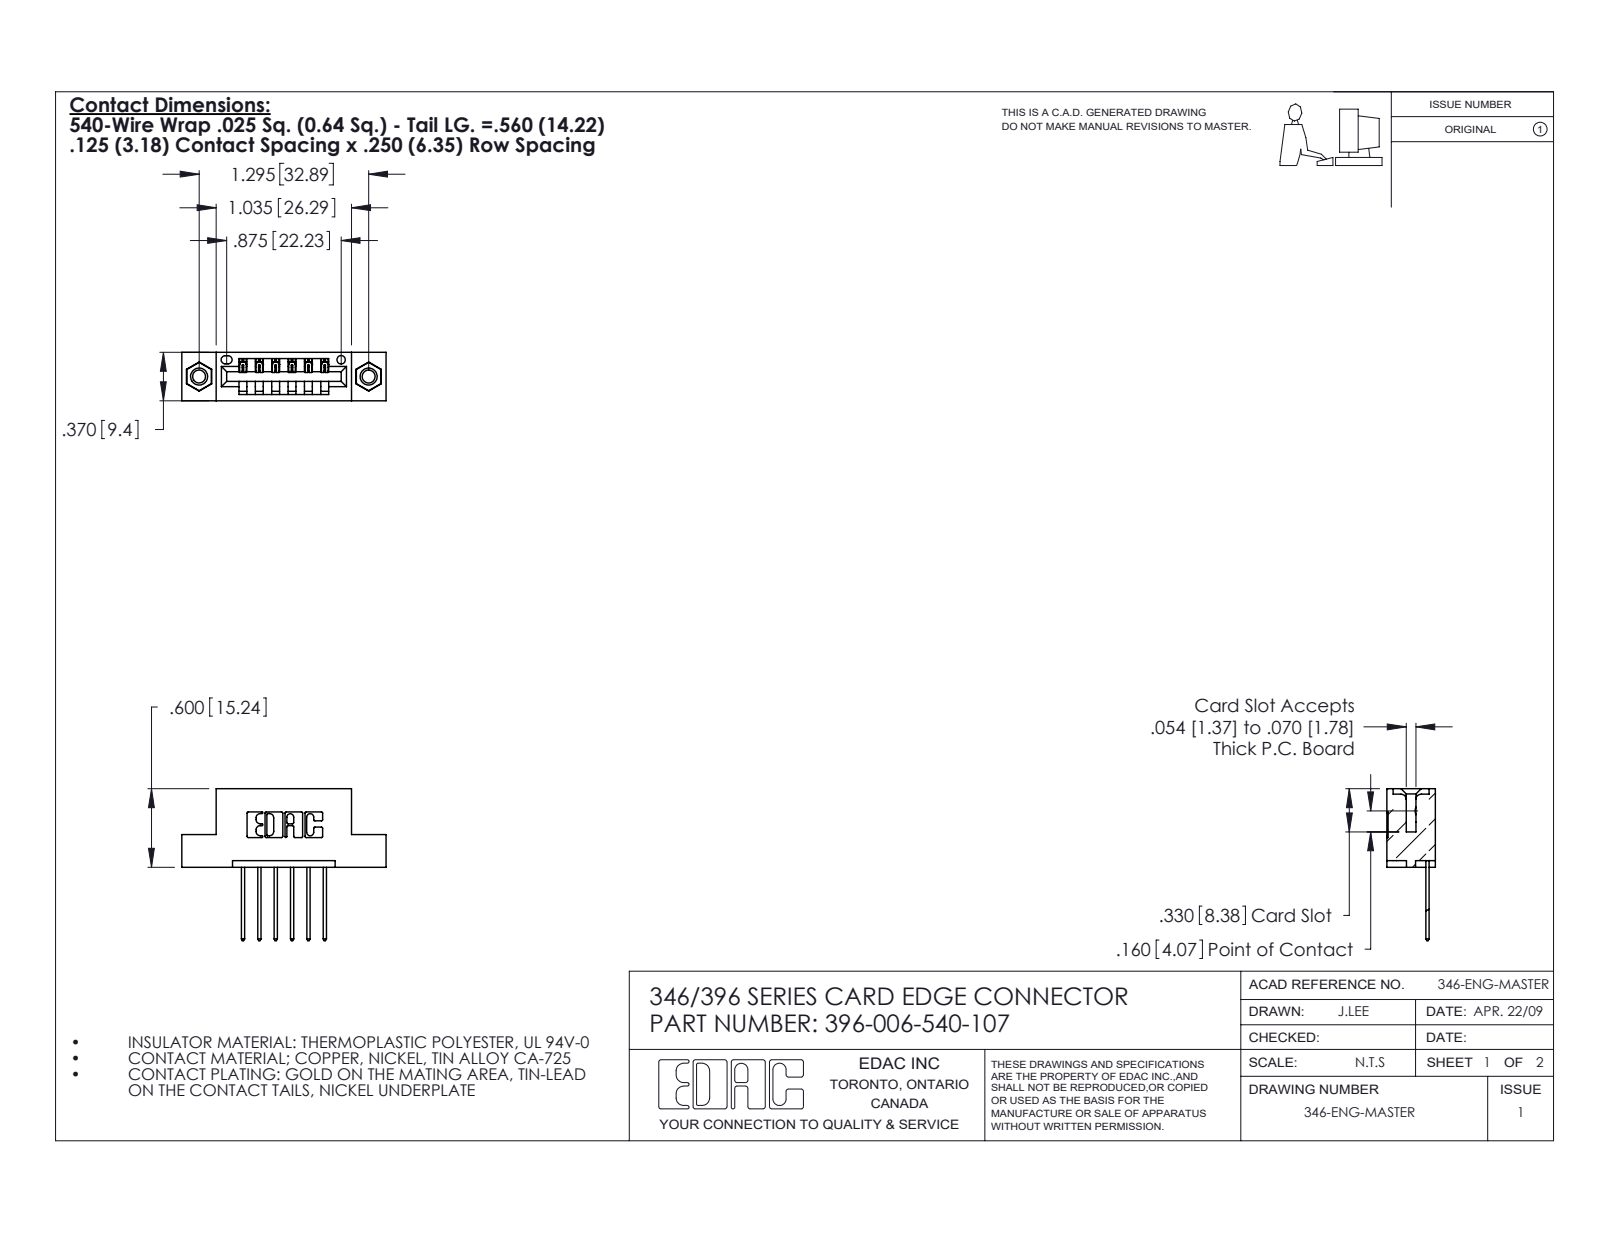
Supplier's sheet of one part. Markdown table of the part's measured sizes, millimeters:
| quantity | value |
| --- | --- |
| part name | 346 Part_Flush Mounting Lugs - 0.156 Dia-TI; 345-250-001_345-250-005-103; 345-292-001_345-293-140; 396-006-540-107 |
| STEP written by | SolidWorks 2020 (CONFIG_CONTROL_DESIGN) |
| units | millimeters |
| bodies | 9 solids, 530 faces (348 planar, 166 cylindrical, 16 other) |
| overall size | 39.6 × 29.5 × 9.4 |
| volume | 3 540 mm³ |
| surface area | 4 130 mm² |
| round holes (diameter × count) | 2.5 × 2, 3.2 × 2, 4 × 2, 1.6 × 1 |
| round bosses / shafts (diameter × count) | 3.9 × 2 |
| partial cylindrical surfaces (radius × count) | 0.3 × 22, 0.2 × 12, 0.3 × 12, 0.2 × 6, 0.8 × 6, 0.7 × 3, 0.8 × 2, 1 × 2 |
| main face-to-face distances | 6.4, 9.4, 1.2, 8.2, 1.8, 7.6, 0.6, 3.8, 5.6, 2.5 |
| hole center spacings | 6.2, 27.7, 32.9 |
